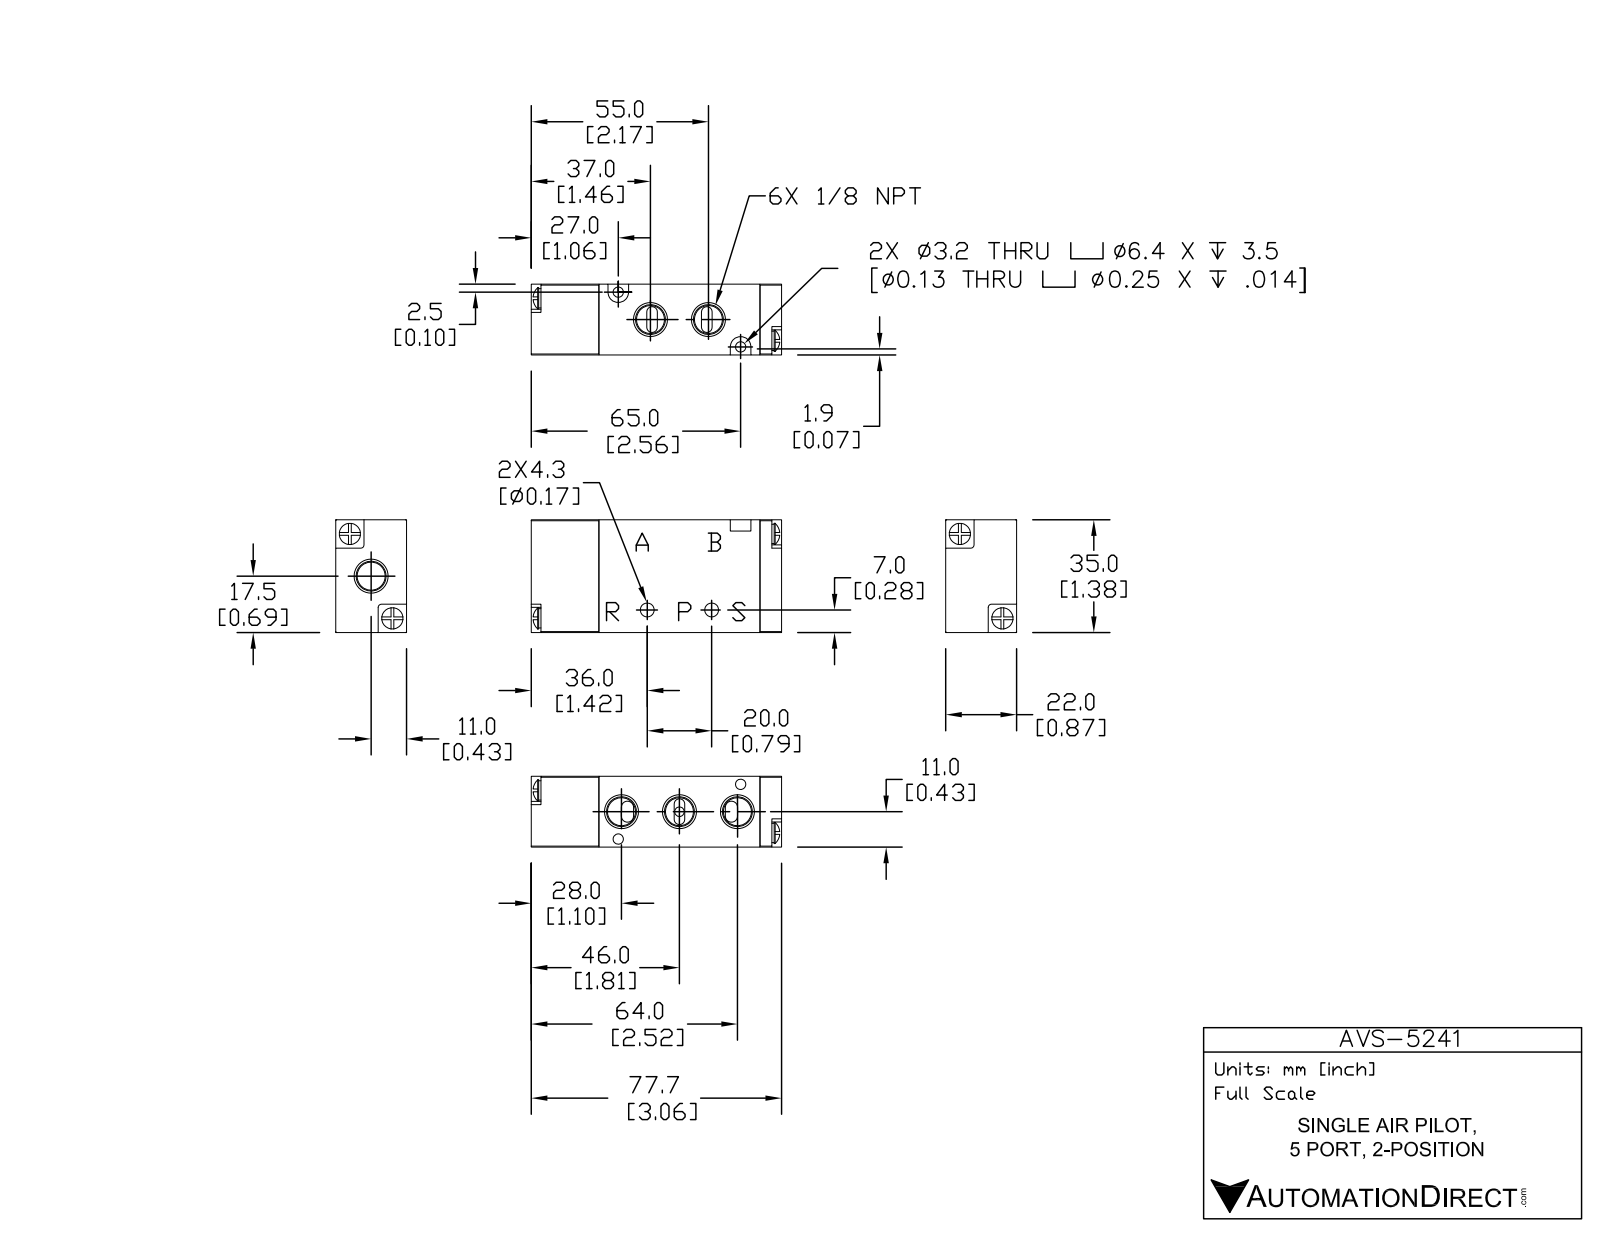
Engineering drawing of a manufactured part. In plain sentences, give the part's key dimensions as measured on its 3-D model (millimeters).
The part is named "AVS-5241". Its 3-D file was written by "SolidWorks 2015 (CONFIG_CONTROL_DESIGN)". It is 3 solids with 194 faces: 98 planar, 56 cylindrical and 40 other. Overall it measures 77.7 by 35 by 22 millimeters. Its volume is 53 420 cubic millimeters and its surface area 16 870 square millimeters. Round holes: 2 of diameter 3.2, 2 of diameter 4.3, 1 of diameter 3. Round bosses or shafts: 4 of diameter 6.6, 4 of diameter 6. Partial cylindrical surfaces (rounded edges, fillets, slot ends): 6 of radius 1.7, 4 of radius 0.3, 4 of radius 1, 4 of radius 1.9, 2 of radius 3.2. The main face-to-face distances are 22, 50, 35, 21, 6.7, 56.7, 77.7, 71, 3, 74.7. The hole center spacings are 20.8, 20, 41.6.
